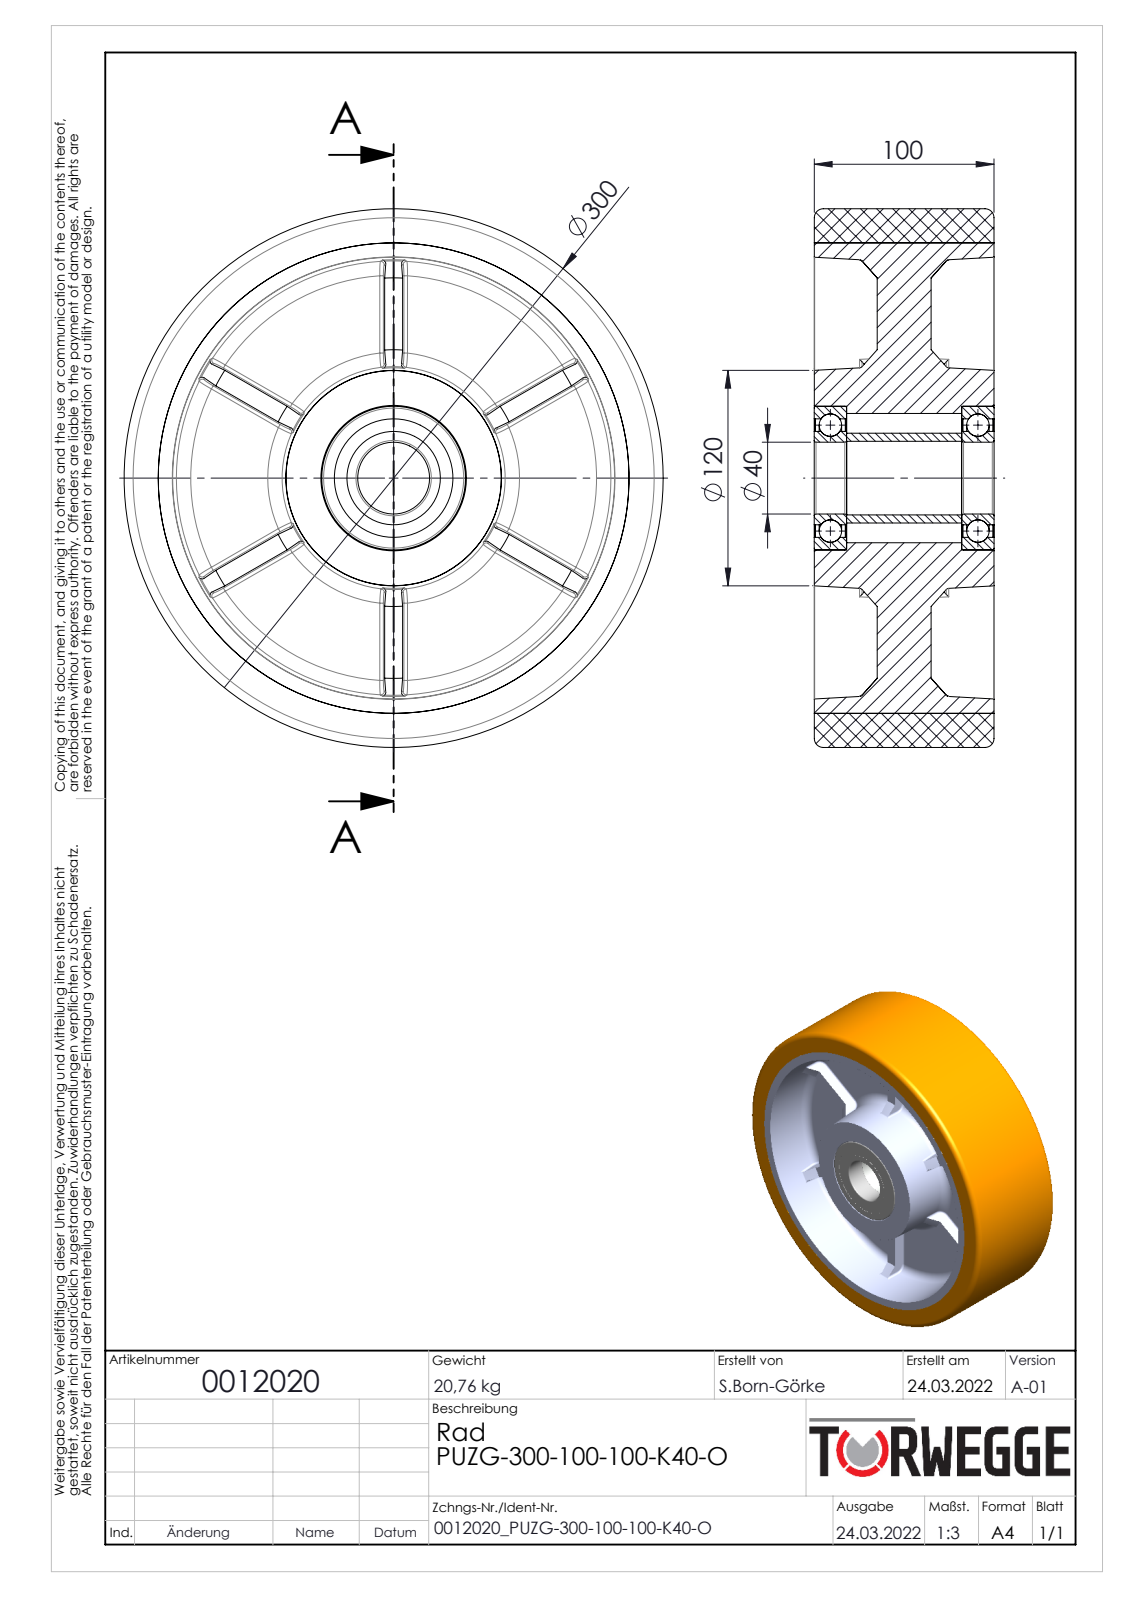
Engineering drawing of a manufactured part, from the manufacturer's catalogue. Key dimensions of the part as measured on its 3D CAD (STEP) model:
Part name (STEP PRODUCT): 0012020
STEP written by: SolidWorks 2020 (AUTOMOTIVE_DESIGN)
Units: millimetres
Bodies: 13 solids, 394 faces (74 planar, 80 cylindrical, 240 other)
Overall size (bounding box): 300 × 300 × 100.1
Volume: 3 761 000 mm³ · Surface area: 594 924 mm²
Round holes (diameter × count): ⌀40 ×1, ⌀41 ×1, ⌀52 ×1, ⌀66 ×1, ⌀72 ×1, ⌀80 ×1, ⌀262 ×1
Round bosses / shafts (diameter × count): ⌀300 ×1, ⌀50 ×1
Partial cylindrical surfaces — rounded edges, fillets, slot ends (radius × count): R2 ×16
Main face-to-face distances: 45, 55, 10, 100, 82.1, 65, 82.05, 18, 12.57, 17.95
